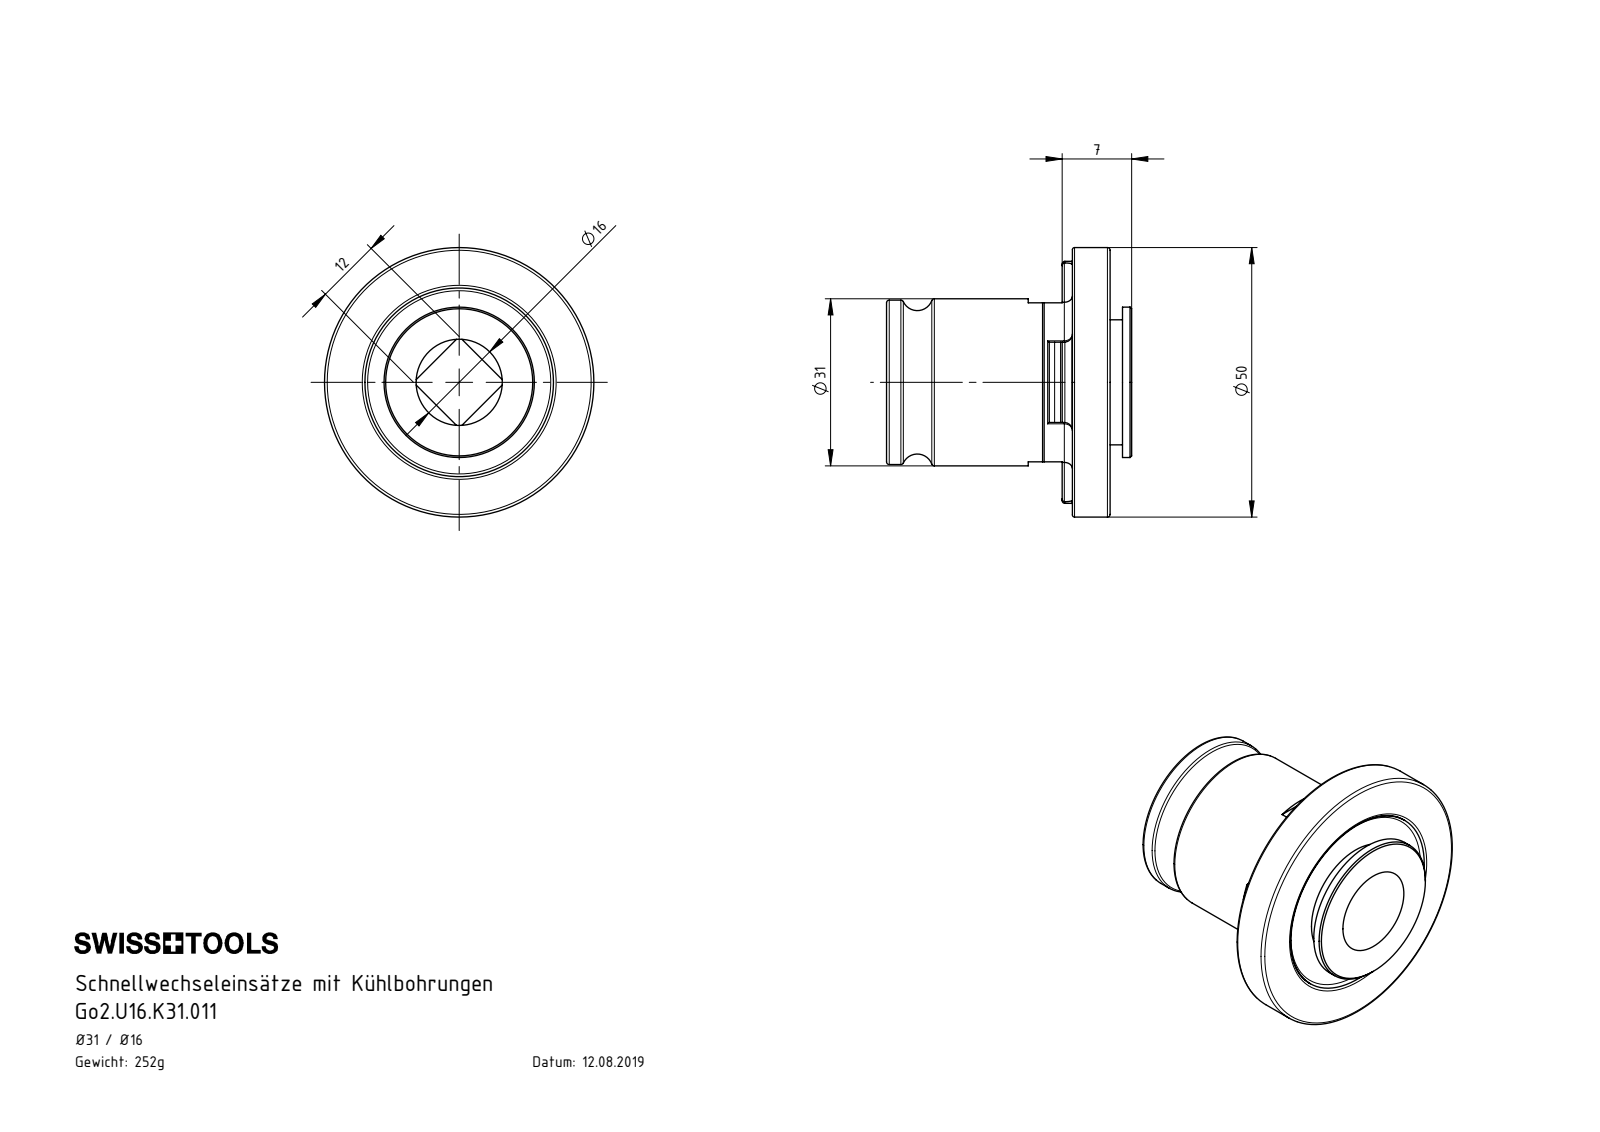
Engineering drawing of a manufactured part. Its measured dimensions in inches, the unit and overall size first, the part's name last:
Units: inches
Overall size (bounding box): 1.969 × 1.969 × 1.791
Round holes (diameter × count): ⌀0.63 ×1, ⌀0.791 ×1
Round bosses / shafts (diameter × count): ⌀1.969 ×1, ⌀1.378 ×1, ⌀1.22 ×1, ⌀1.205 ×1, ⌀1.201 ×1, ⌀1.024 ×1, ⌀0.874 ×1
Partial cylindrical surfaces — rounded edges, fillets, slot ends (radius × count): R0.059 ×5, R0.02 ×4, R0.787 ×1, R0.884 ×1
Main face-to-face distances: 0.276, 0.25, 0.026, 1.358, 1.608, 1.634, 1.791, 0.433, 0.183, 0.157
Volume: 1.948 in³ · Surface area: 17.34 in²
Bodies: 1 solid, 133 faces (37 planar, 39 cylindrical, 57 other)
Part name (STEP PRODUCT): Go2.U16.K31.011
STEP written by: SolidWorks 2012 (AUTOMOTIVE_DESIGN)
